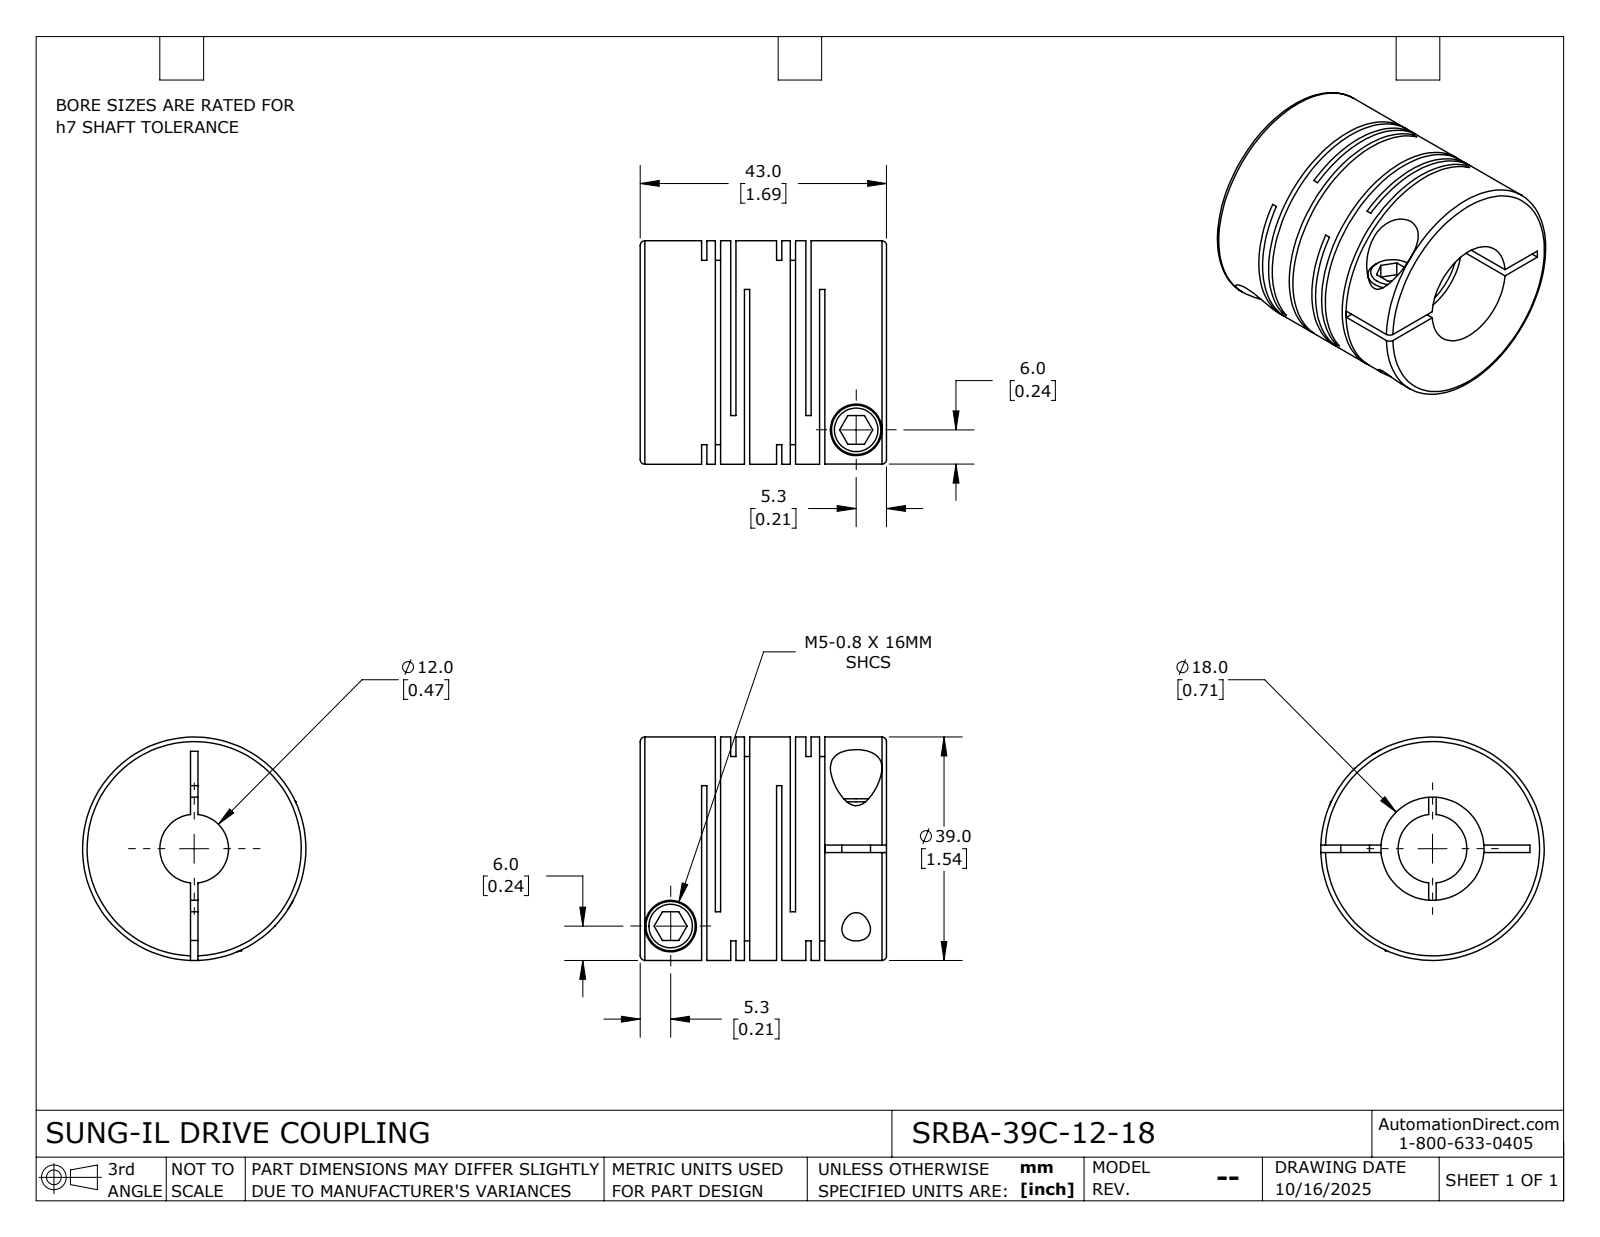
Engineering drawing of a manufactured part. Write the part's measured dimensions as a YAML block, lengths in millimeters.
part_name: "SRBA-39C-12-18"
step_written_by: "SolidWorks 2024 (CONFIG_CONTROL_DESIGN)"
units: millimeters
bodies: {solids: 1, faces: 115, planar: 60, cylindrical: 42, other: 13}
overall_size: [43, 39, 39]
volume: 34944
surface_area: 22323
round_holes:
  - {diameter: 5, count: 2}
  - {diameter: 9, count: 2}
  - {diameter: 12, count: 1}
  - {diameter: 18, count: 1}
round_bosses_or_shafts:
  - {diameter: 8.6, count: 2}
  - {diameter: 39, count: 1}
face_to_face_distances: [13.1, 0.92, 2.4, 5.1, 10.7, 14.02, 18.2, 7.5, 12.18, 3.32]
